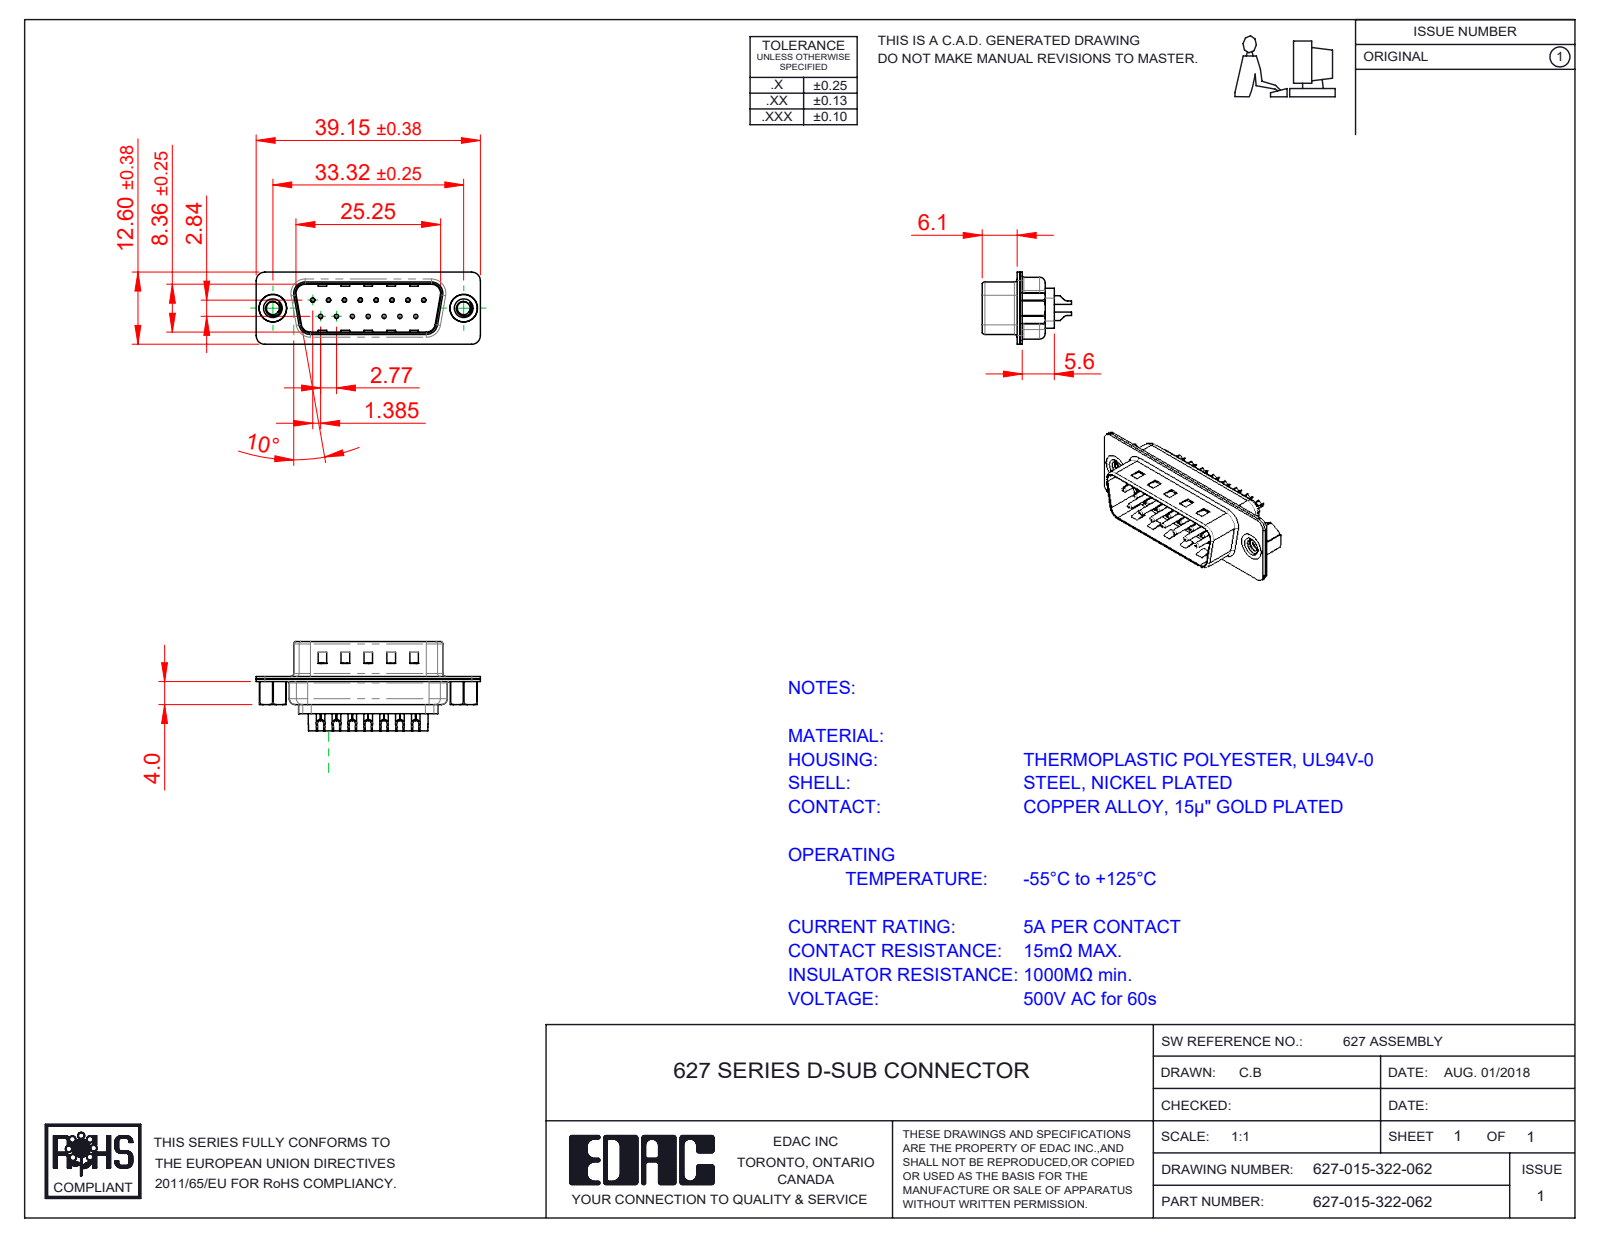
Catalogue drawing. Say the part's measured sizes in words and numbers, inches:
The part is named "627 Shell Front_15 Contacts; 627-015-322-062; 627 Contact Row 1_22L; 627 4-40 Threaded Rivet (+3 more)". Its 3-D file was written by "SolidWorks 2020 (CONFIG_CONTROL_DESIGN)". It is 20 solids with 1296 faces: 349 planar, 566 cylindrical and 381 other. Overall it measures 1.541 by 0.604 by 0.496 inches. Its volume is 0.112 cubic inches and its surface area 8.39 square inches. Round holes: 15 of diameter 0.014, 15 of diameter 0.043, 15 of diameter 0.063, 2 of diameter 0.089, 2 of diameter 0.157, 2 of diameter 0.189. Round bosses or shafts: 15 of diameter 0.079, 15 of diameter 0.059, 15 of diameter 0.03, 2 of diameter 0.197, 2 of diameter 0.193. Partial cylindrical surfaces (rounded edges, fillets, slot ends): 16 of radius 0.059, 12 of radius 0.079, 8 of radius 0.02, 8 of radius 0.063, 6 of radius 0.039, 4 of radius 0.01, 4 of radius 0.024, 4 of radius 0.026. The main face-to-face distances are 0.016, 0.018, 0.035, 0.032, 0.377, 0.345, 0.059, 0.055, 0.256, 0.22. The hole center spacings are 0.124, 0.109, 0.218, 0.327, 0.436, 0.198, 0.198, 0.294.
